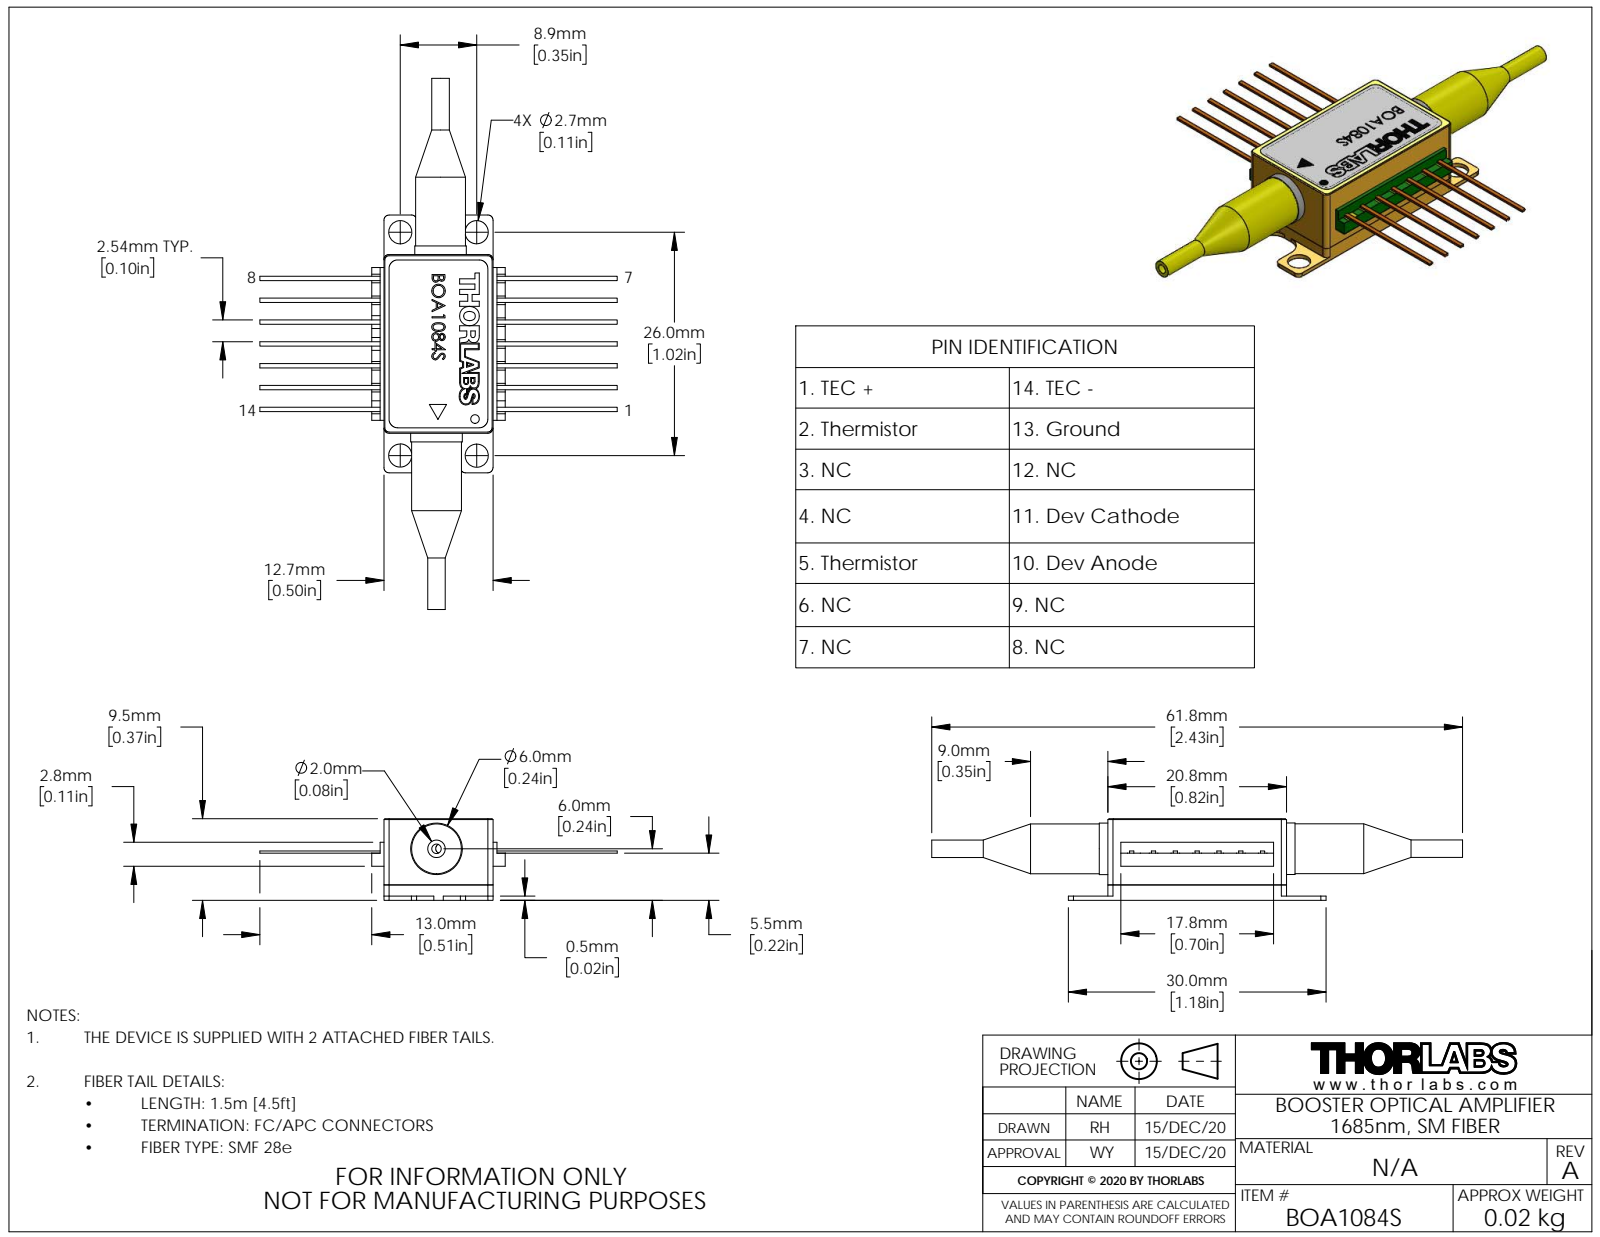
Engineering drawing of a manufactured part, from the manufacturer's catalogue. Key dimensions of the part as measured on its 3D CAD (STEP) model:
Part name (STEP PRODUCT): QTN040858-E0W
STEP written by: SolidWorks 2018 (AUTOMOTIVE_DESIGN)
Units: inches
Bodies: 0 solids, 350 faces (249 planar, 53 cylindrical, 48 other)
Overall size (bounding box): 2.433 × 1.638 × 0.374
Round holes (diameter × count): ⌀0.106 ×4, ⌀0.043 ×2, ⌀0.039 ×1
Round bosses / shafts (diameter × count): ⌀0.236 ×2, ⌀0.228 ×2, ⌀0.08 ×2
Partial cylindrical surfaces — rounded edges, fillets, slot ends (radius × count): R0.024 ×12, R0.02 ×4, R0.079 ×4, R0.039 ×3
Main face-to-face distances: 0.373, 0.5, 0.156, 0.217, 0.06, 0.217, 0.157, 0.02, 0.226, 0.07
Hole centre spacings: 0.35, 1.024, 1.082, 0.019, 0.168, 0.382, 0.856, 0.922
